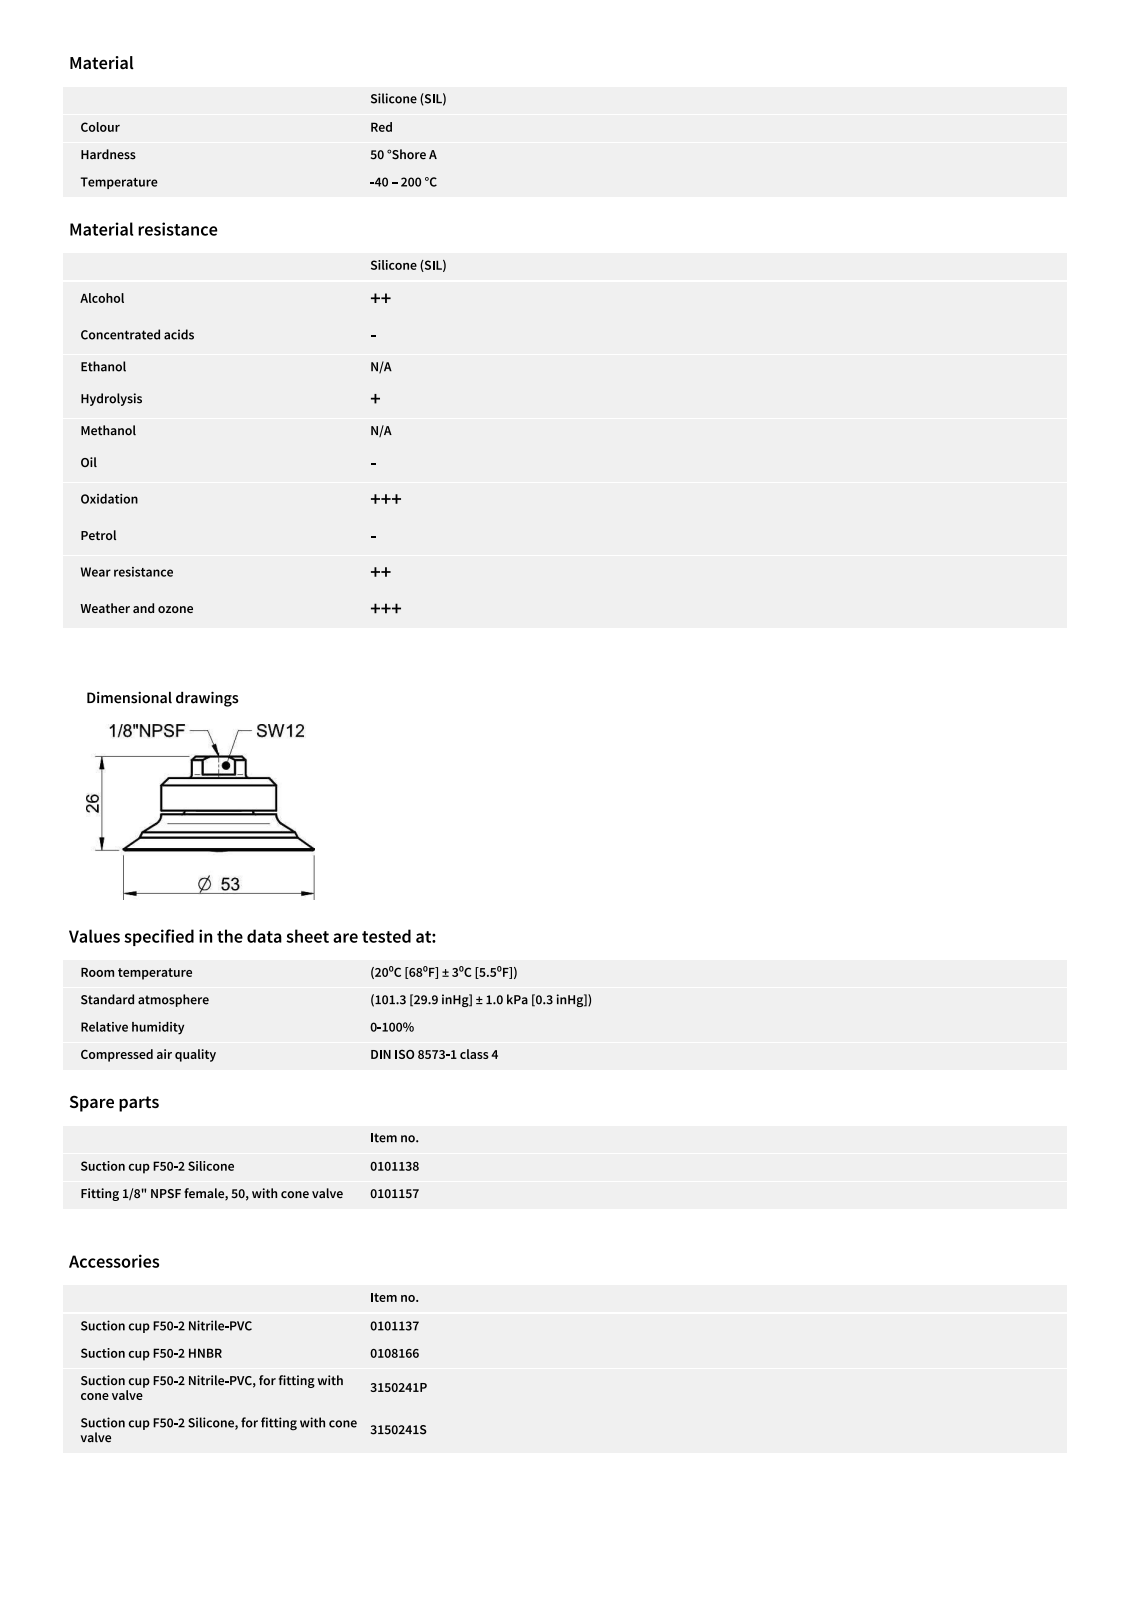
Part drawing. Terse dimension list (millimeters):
name: SE-0412759; 0101086; 3150198
written by: Unknown (AUTOMOTIVE_DESIGN)
unit: mm
bodies: 3 solids, 147 faces (83 planar, 30 cylindrical, 34 other)
size: 53 × 53 × 26.5
volume: 19 306 mm³; area: 10 110 mm²
holes: 1× ⌀8.7, 1× ⌀10.5, 1× ⌀12.5, 1× ⌀14, 1× ⌀19.5
bosses: 1× ⌀32, 1× ⌀28, 1× ⌀27, 1× ⌀19, 1× ⌀15, 1× ⌀12
rounds: 8× R0.17, 6× R0.5, 2× R0.42
face distances: 17.5, 3.5, 4, 7.5, 14, 10, 0.5, 7, 10.5, 11
